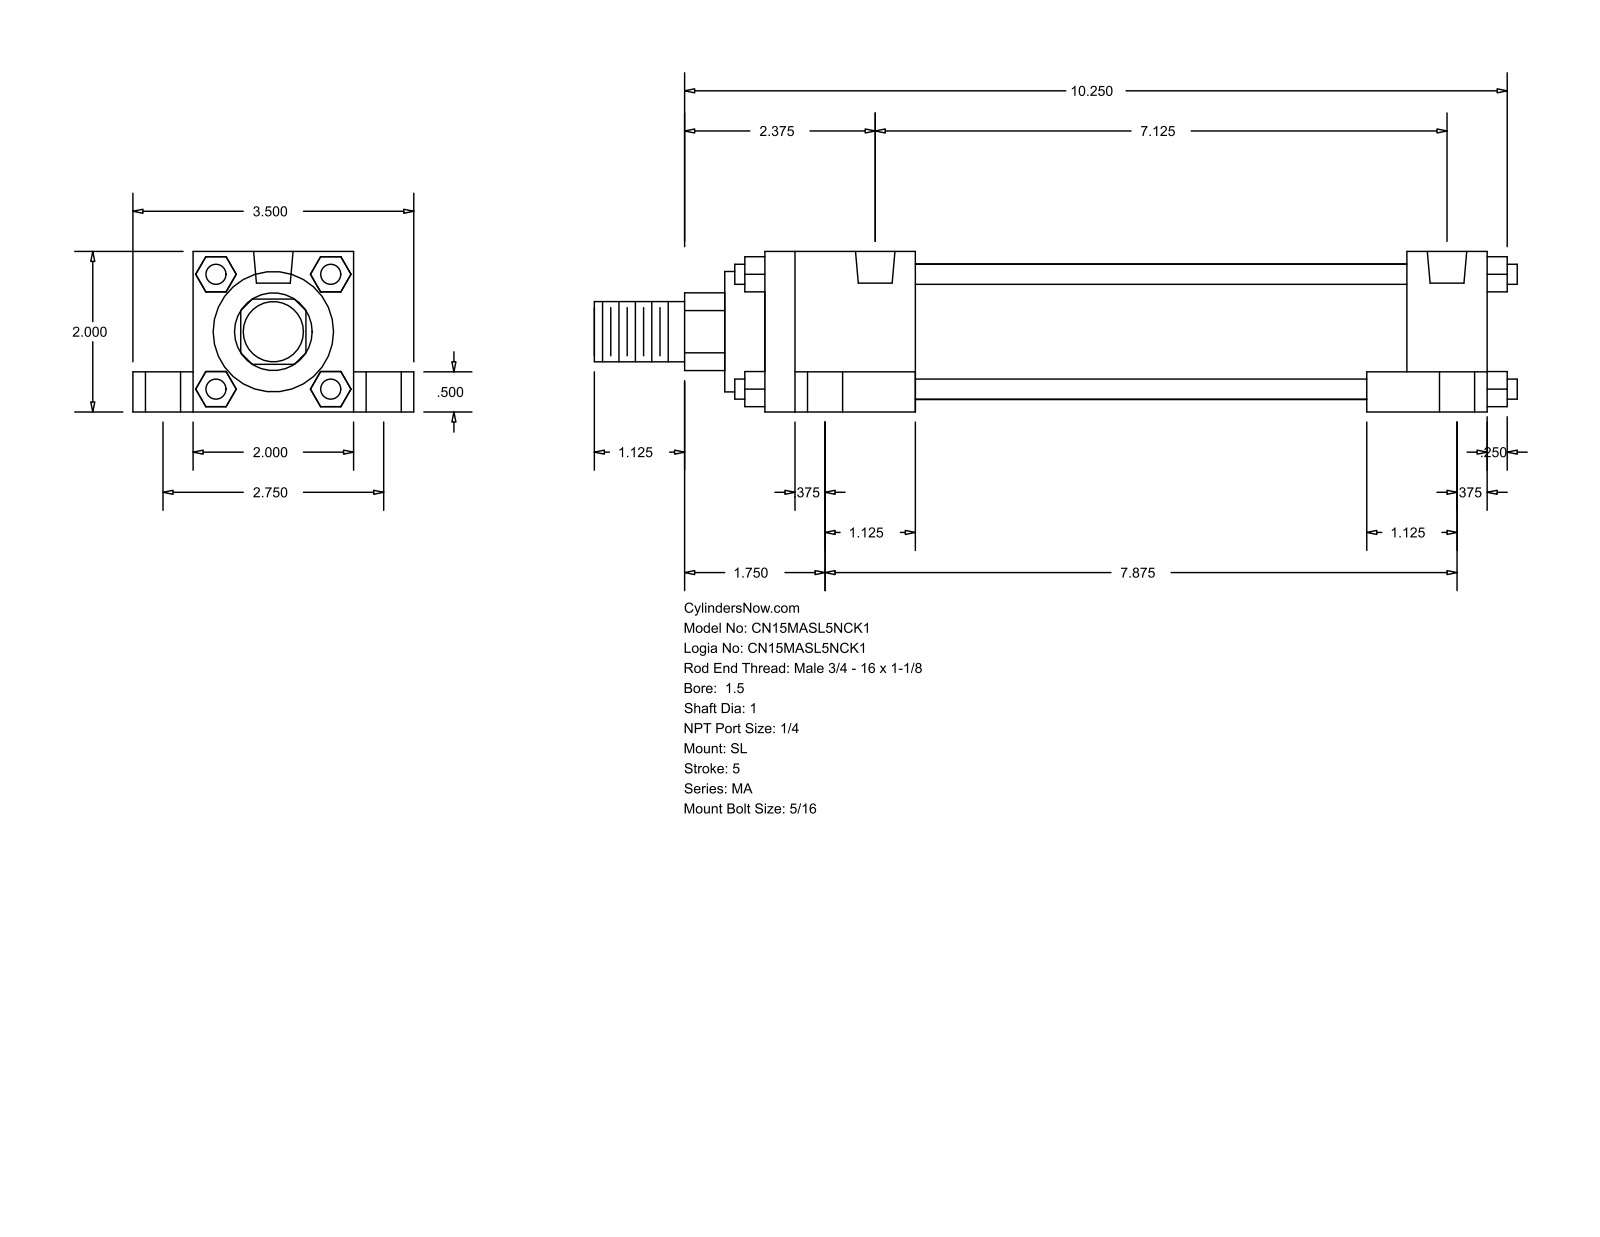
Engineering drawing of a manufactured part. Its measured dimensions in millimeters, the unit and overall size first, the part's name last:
Units: millimetres
Overall size (bounding box): 292.1 × 88.9 × 50.8
Round holes (diameter × count): ⌀7.94 ×4, ⌀11.11 ×4, ⌀17.46 ×4, ⌀12.49 ×2
Round bosses / shafts (diameter × count): ⌀6.35 ×4, ⌀42.93 ×1, ⌀38.1 ×1, ⌀25.4 ×1, ⌀19.05 ×1
Partial cylindrical surfaces — rounded edges, fillets, slot ends (radius × count): R12.29 ×1
Main face-to-face distances: 50.8, 12.7, 19.05, 69.85, 38.1, 9.52, 228.6, 25.4, 6.35, 203.2
Hole centre spacings: 35.06, 38.36, 69.84, 180.97, 187.42, 199.92, 200.02, 211.86
Bodies: 0 solids, 148 faces (112 planar, 36 cylindrical, 0 other)
Part name (STEP PRODUCT): MA_SL__0150_1
STEP written by: GSSL Pune (CONFIG_CONTROL_DESIGN)
